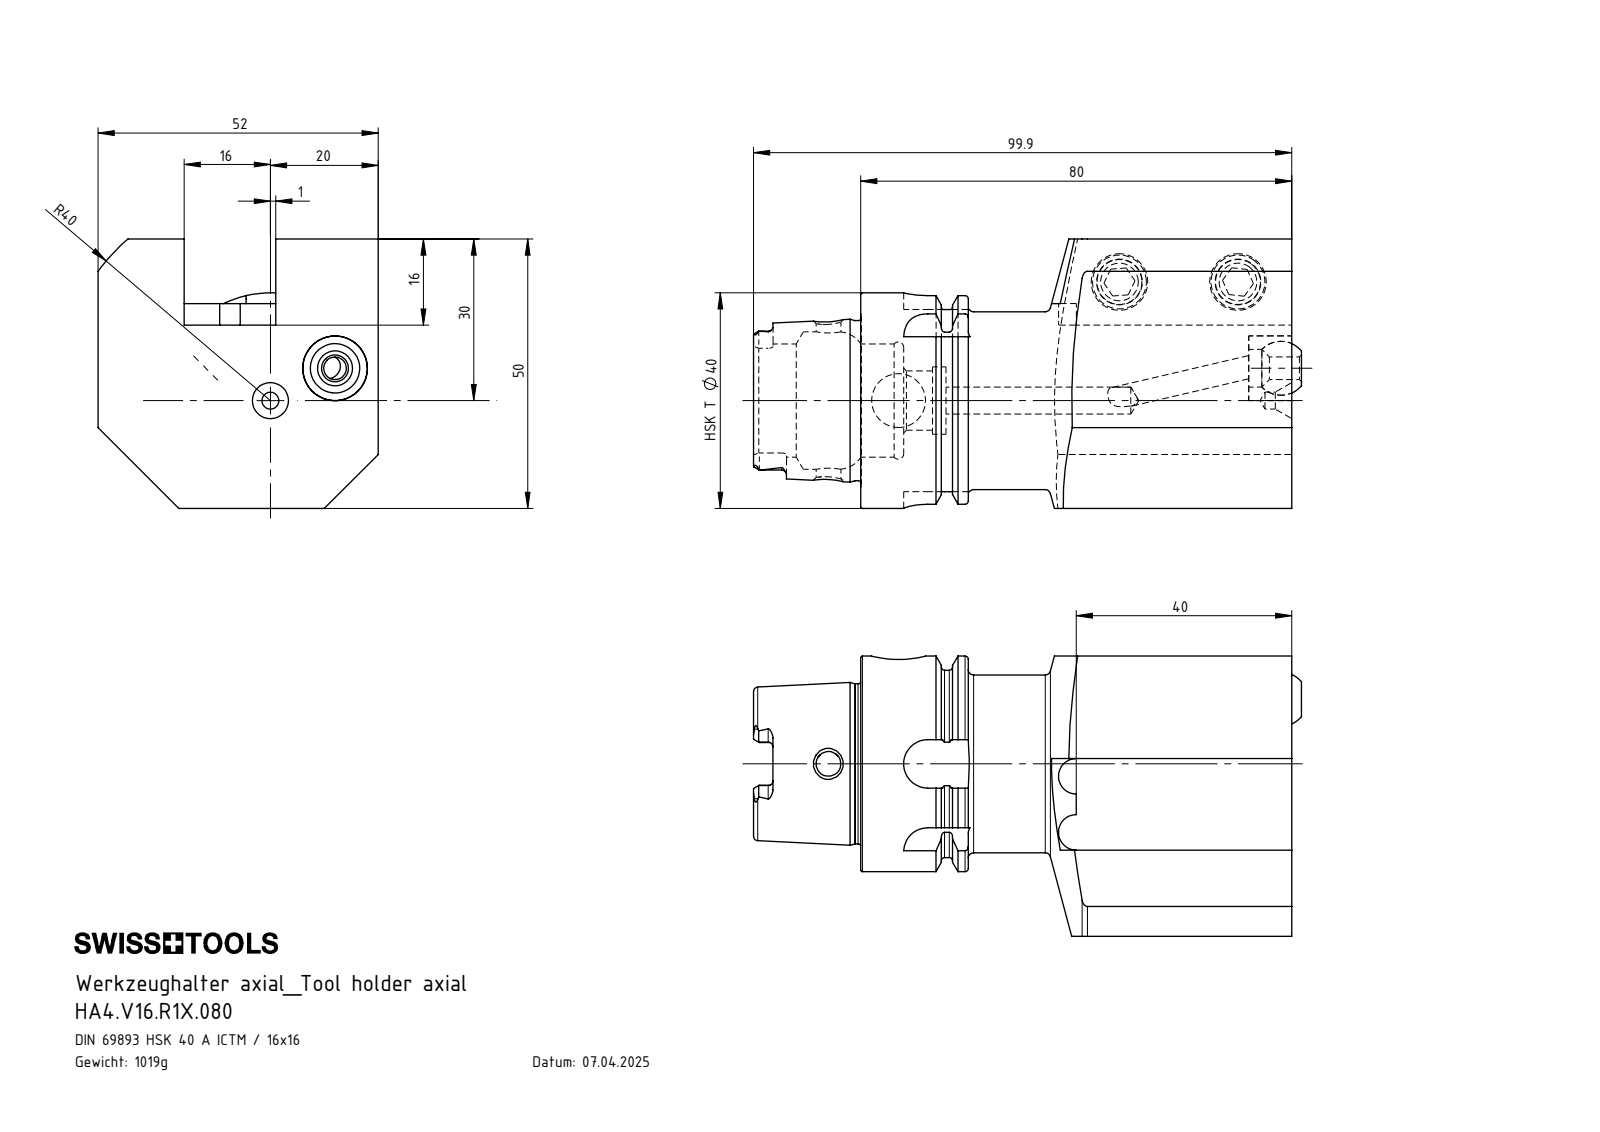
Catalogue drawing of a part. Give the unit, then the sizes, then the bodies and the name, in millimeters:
Units: millimetres
Overall size (bounding box): 101.7 × 52 × 50
Round holes (diameter × count): ⌀4.2 ×2, ⌀8.5 ×2, ⌀3.15 ×1, ⌀4.6 ×1, ⌀5 ×1, ⌀7 ×1, ⌀10 ×1, ⌀11 ×1, ⌀12 ×1, ⌀12.5 ×1, ⌀21 ×1, ⌀25.5 ×1
Round bosses / shafts (diameter × count): ⌀10 ×2, ⌀40 ×1, ⌀34.75 ×1, ⌀33 ×1, ⌀29.71 ×1
Partial cylindrical surfaces — rounded edges, fillets, slot ends (radius × count): R0.9 ×6, R1.88 ×4, R4.5 ×4, R3.3 ×2, R40 ×1
Main face-to-face distances: 16, 50, 52, 34, 36, 19, 17, 33, 80, 12
Hole centre spacings: 13.42, 22, 46.53, 66.73
Volume: 130 100 mm³ · Surface area: 27 485 mm²
Bodies: 5 solids, 247 faces (80 planar, 71 cylindrical, 96 other)
Part name (STEP PRODUCT): KU1-U12.001.010; KU1-U12.001.010_2; ISO 4026 - M10 x 18; KU1-U12.001.010_1 (+2 more)
STEP written by: SolidWorks 2022 (AUTOMOTIVE_DESIGN)
